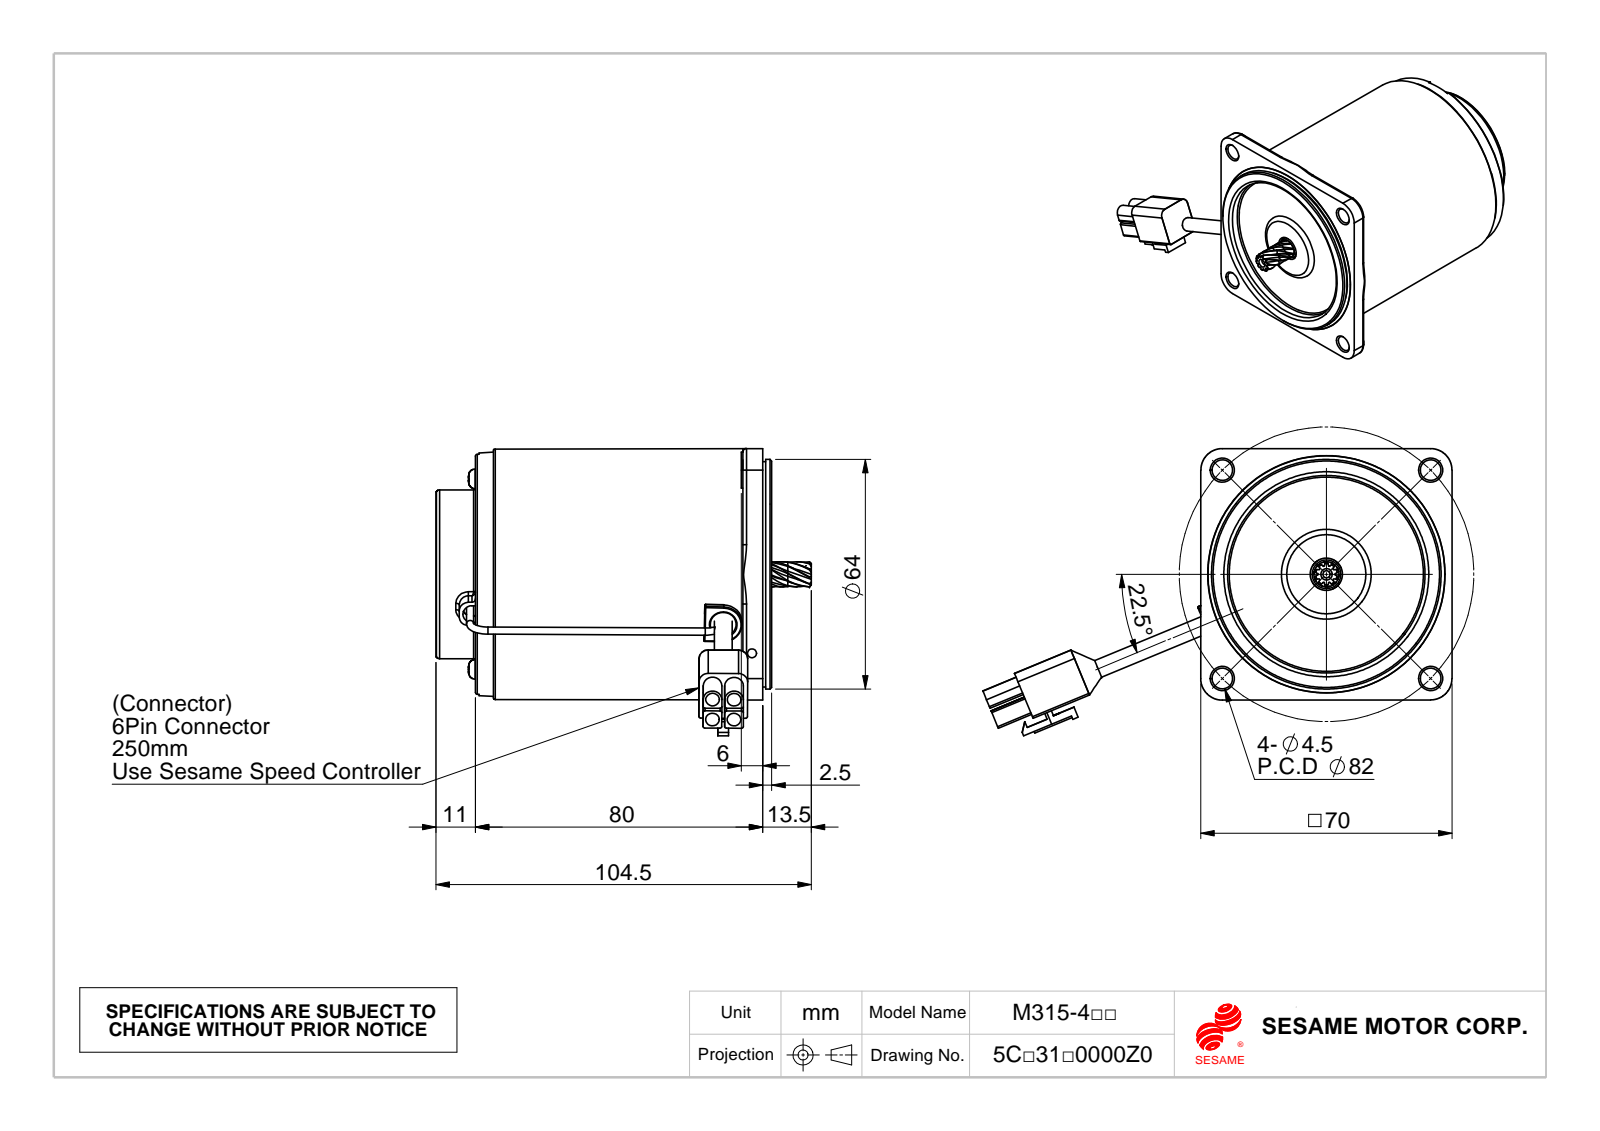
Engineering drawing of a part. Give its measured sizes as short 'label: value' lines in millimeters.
name: 線扣; M315-RK-R-模型_3.鑽孔; 公端子; C364_車工(成品) (+1 more)
written by: SolidWorks 2010 (CONFIG_CONTROL_DESIGN)
unit: mm
bodies: 9 solids, 516 faces (172 planar, 181 cylindrical, 163 other)
size: 130.68 × 104.5 × 79.96
volume: 336 988 mm³; area: 51 552 mm²
holes: 5× ⌀2.5, 4× ⌀3.8, 4× ⌀4.2, 4× ⌀5.5, 4× ⌀5.75, 2× ⌀2, 2× ⌀3.1, 1× ⌀7.2, 1× ⌀9, 1× ⌀9.5, 1× ⌀15, 1× ⌀18
bosses: 4× ⌀10, 2× ⌀5.5, 2× ⌀3, 2× ⌀2, 1× ⌀63.93, 1× ⌀62.73, 1× ⌀58, 1× ⌀57.42
rounds: 14× R0.5, 10× R1, 8× R0.25, 8× R0.3, 7× R2.5, 4× R6, 2× R2.6, 1× R5.25
face distances: 77.4, 77.5, 1.51, 75.89, 1.61, 1.5, 1.6, 79, 3.11, 12
hole spacings: 43.34, 6, 14, 4.24, 10.72, 19.33, 19.8, 25.87
